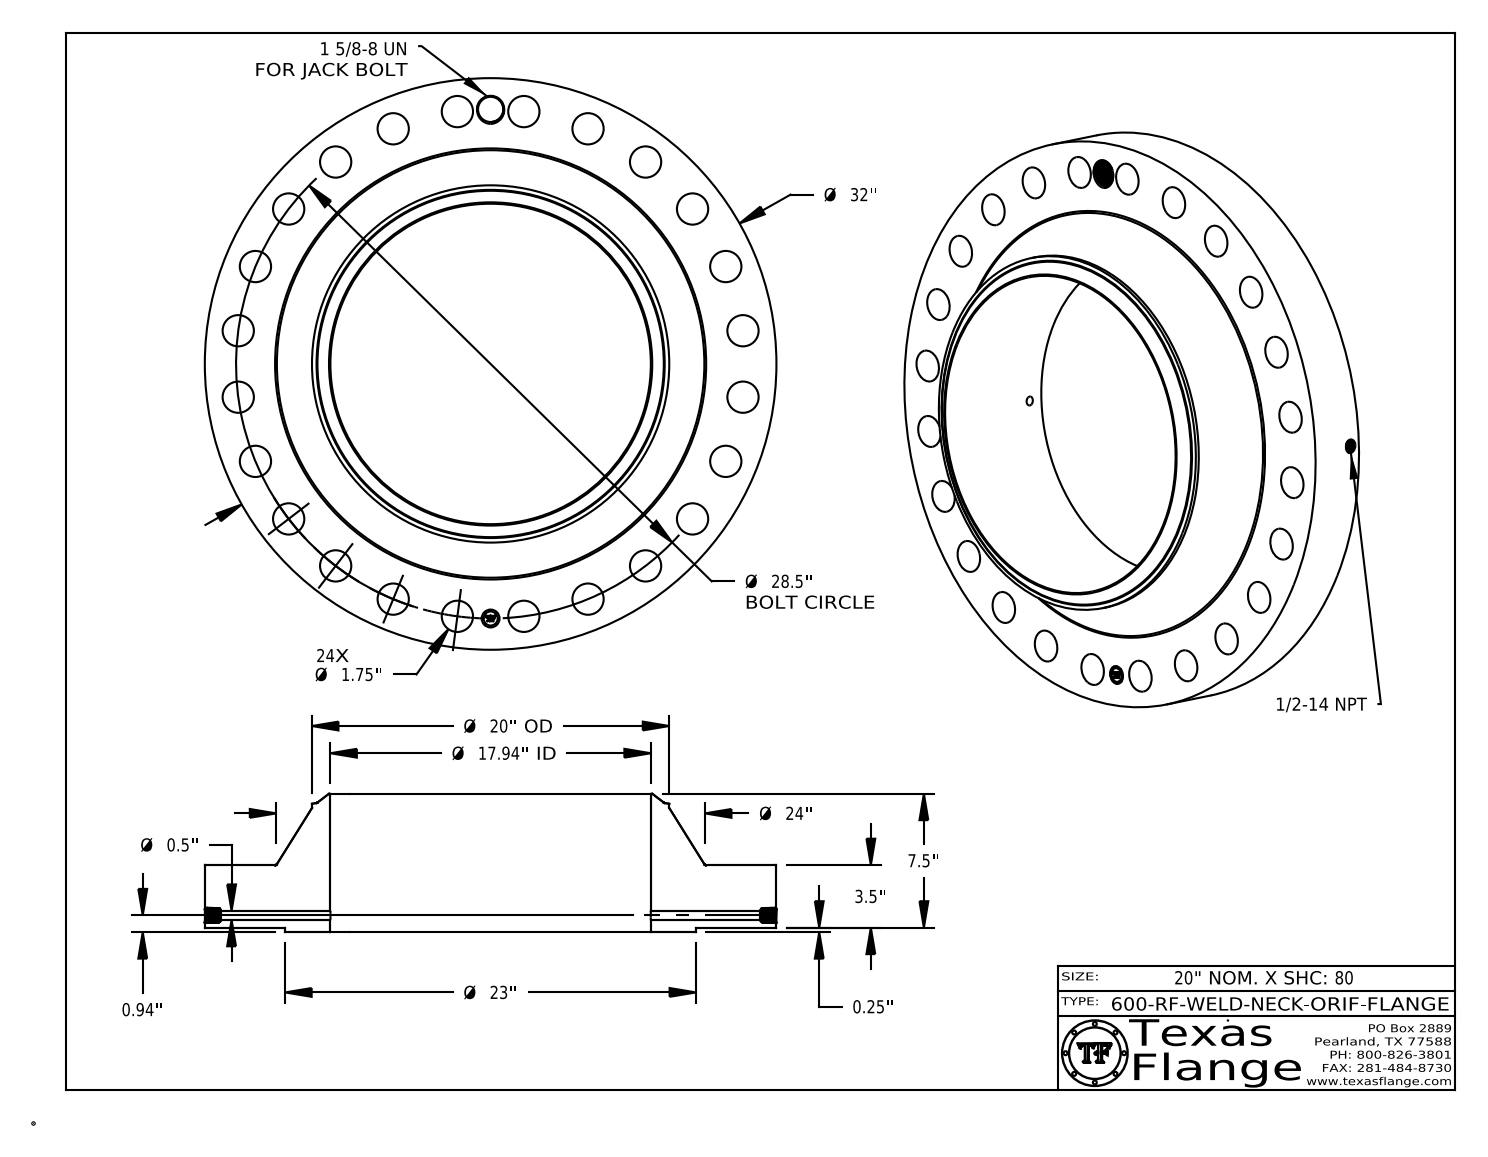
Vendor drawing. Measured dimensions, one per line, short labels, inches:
name: 600-RF-WELD-NECK
written by: CATIA V5 STEP AP214 (AUTOMOTIVE_DESIGN)
unit: in
bodies: 1 solid, 883 faces (369 planar, 151 cylindrical, 363 other)
size: 32 × 32 × 7.75
volume: 2 200 in³; area: 2 458 in²
holes: 24× ⌀1.75, 1× ⌀0.5, 1× ⌀0.672, 1× ⌀1, 1× ⌀1.409, 1× ⌀17.938
bosses: 8× ⌀0.061, 1× ⌀32, 1× ⌀23, 1× ⌀20, 1× ⌀0.788
face distances: 3.5, 0.25, 3.75, 7.75, 7.5, 4, 3.735, 3.485, 0.015, 4.015
hole spacings: 14.25, 17.35, 24.681, 28.256, 10.906, 3.72, 7.376, 20.152
